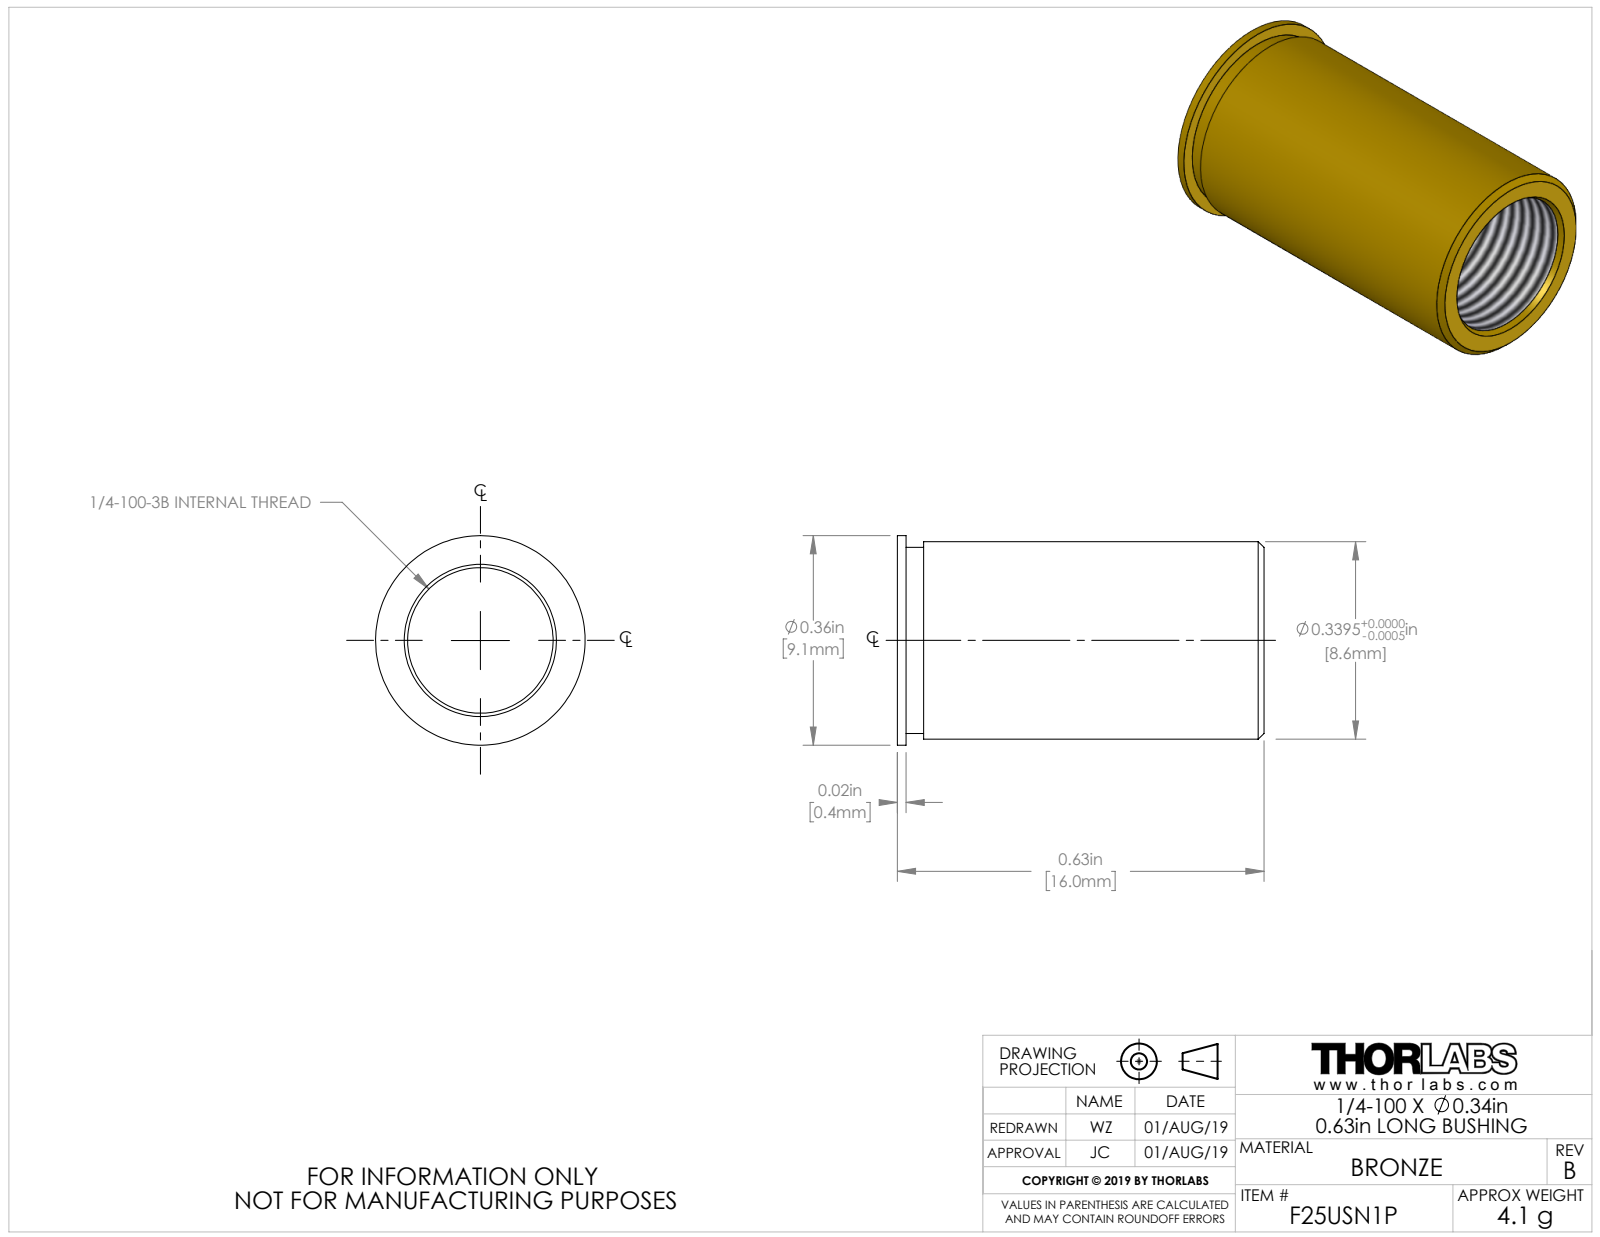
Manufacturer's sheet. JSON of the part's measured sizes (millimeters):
{"part_name": "18993-E0W", "step_written_by": "SolidWorks 2011 (AUTOMOTIVE_DESIGN)", "units": "millimeters", "bodies": {"solids": 1, "faces": 18, "planar": 4, "cylindrical": 8, "other": 6}, "overall_size": [16, 9.1, 9.1], "volume_mm3": 430, "surface_area_mm2": 825, "round_holes": [[6.4, 1]], "round_bosses_or_shafts": [[9.1, 1], [8.6, 1], [8.1, 1]], "face_to_face_distances": [16, 0.4, 15.6, 1.1, 0.8, 14.9]}
